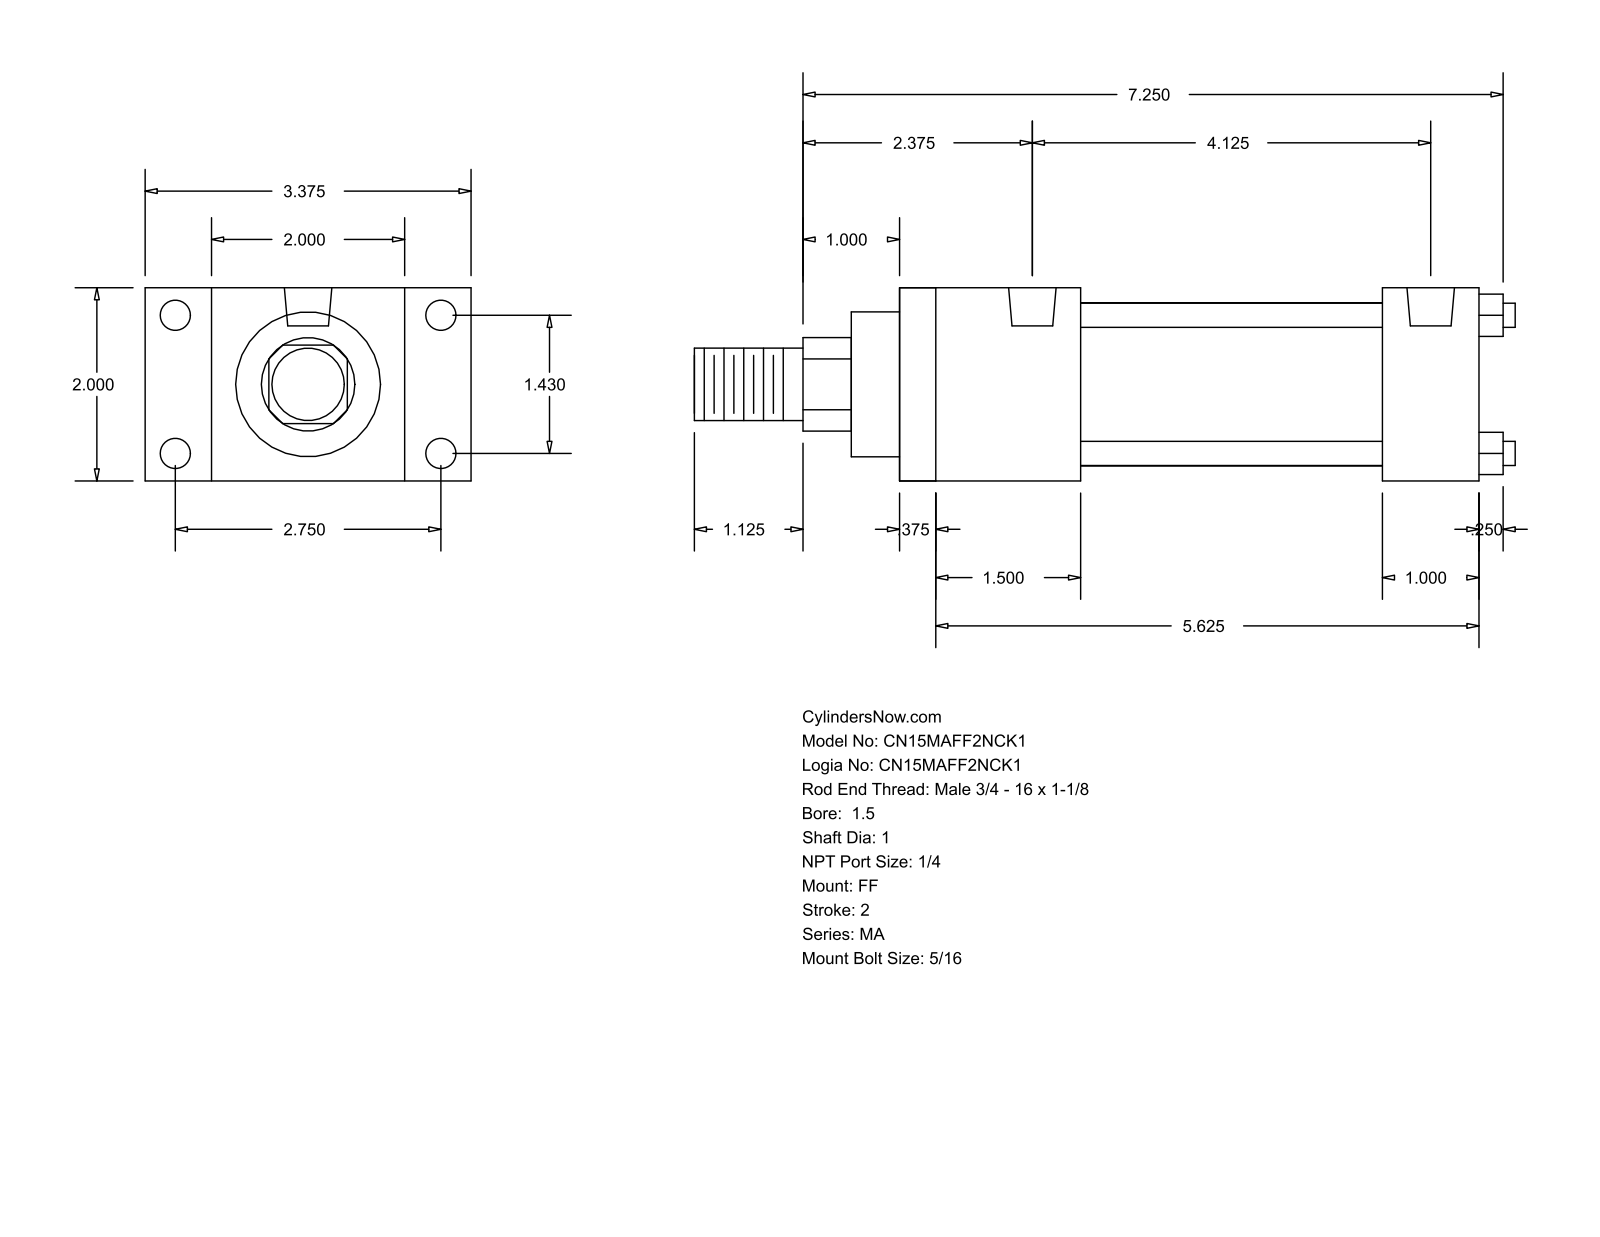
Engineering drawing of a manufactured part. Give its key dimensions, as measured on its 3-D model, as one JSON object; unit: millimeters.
{"part_name": "MA_FF__0150_1", "step_written_by": "GSSL Pune (CONFIG_CONTROL_DESIGN)", "units": "millimeters", "bodies": {"solids": 0, "faces": 92, "planar": 64, "cylindrical": 28, "other": 0}, "overall_size": [215.9, 85.72, 50.8], "round_holes": [[7.94, 8], [12.49, 2]], "round_bosses_or_shafts": [[6.35, 4], [42.93, 1], [38.1, 1], [25.4, 1], [19.05, 1]], "partial_cylinders_radius": [[12.29, 1]], "face_to_face_distances": [50.8, 152.4, 9.52, 142.88, 25.4, 47.63, 127, 38.11, 117.48, 79.37], "hole_center_spacings": [36.32, 69.84, 78.72, 104.77]}
